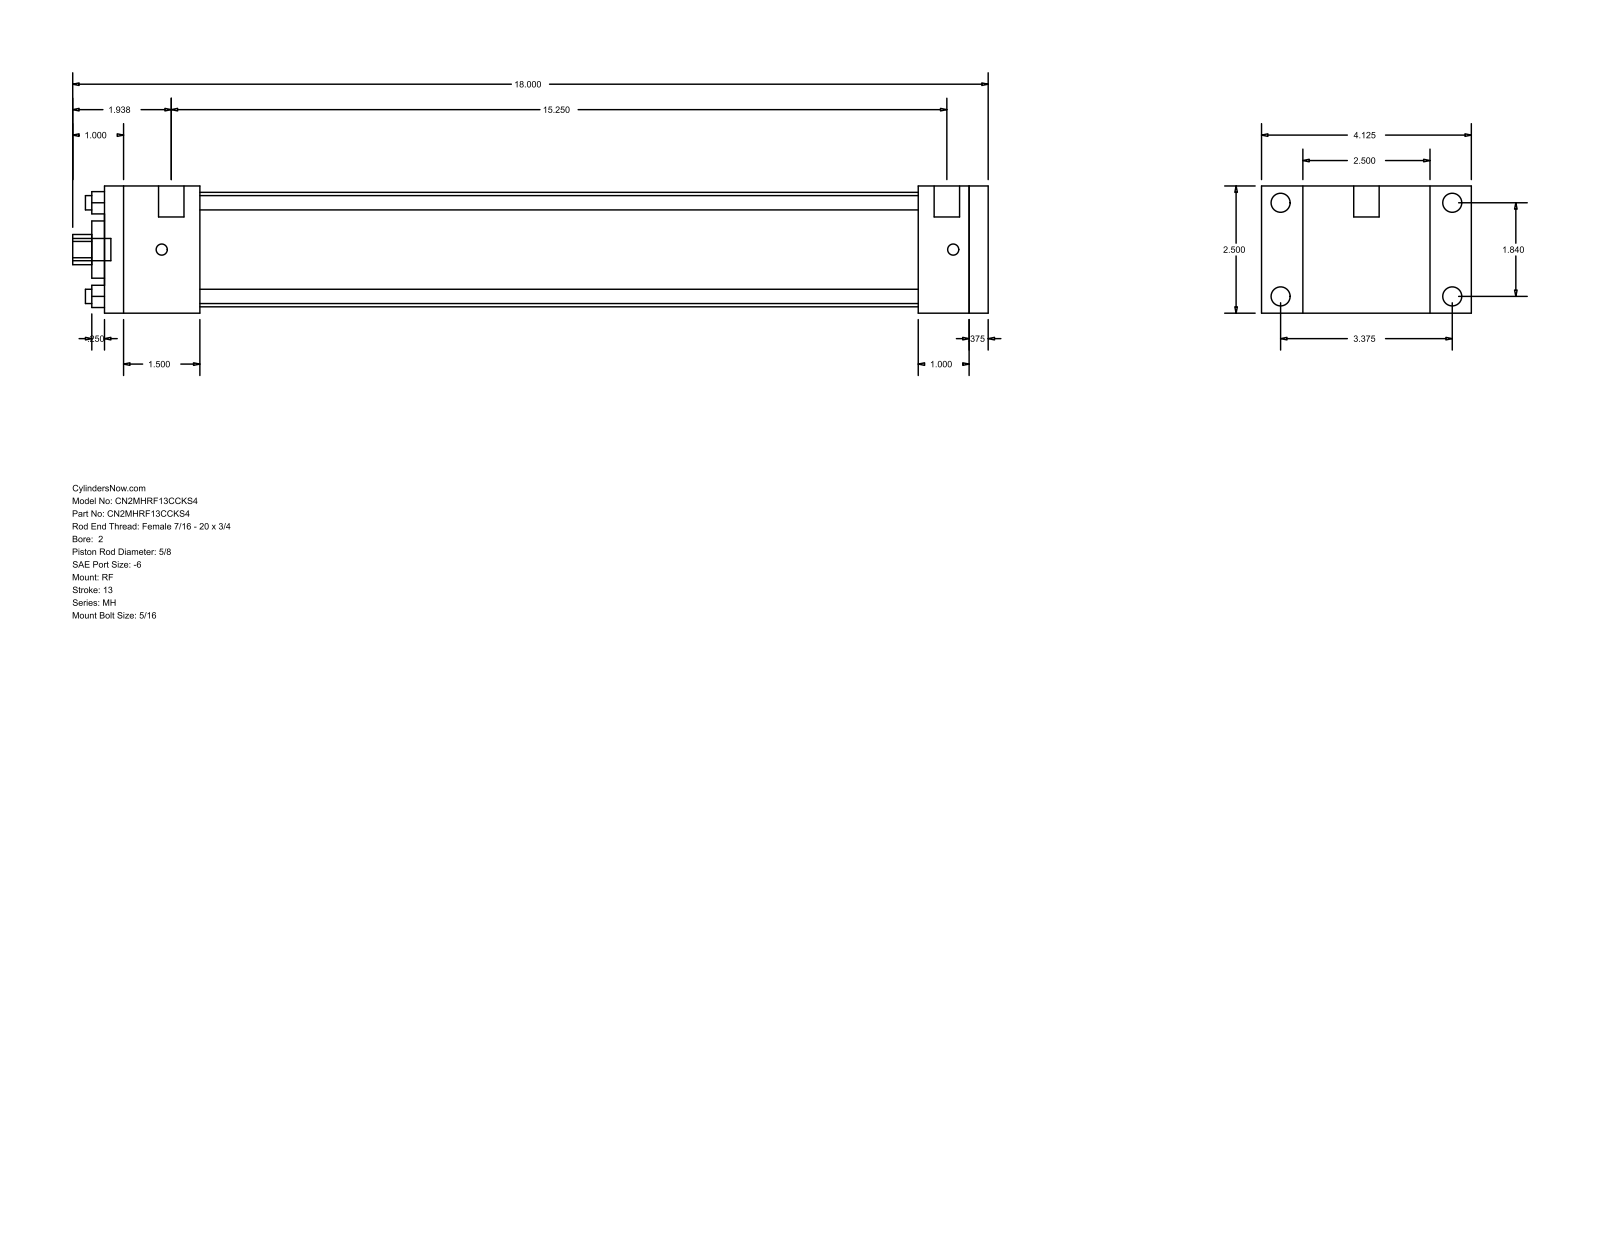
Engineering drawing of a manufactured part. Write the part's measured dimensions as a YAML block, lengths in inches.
part_name: "MH_RF__0200_0.625"
step_written_by: "GSSL Pune (CONFIG_CONTROL_DESIGN)"
units: inches
bodies: {solids: 0, faces: 92, planar: 64, cylindrical: 28, other: 0}
overall_size: [18, 4.125, 2.5]
round_holes:
  - {diameter: 0.281, count: 4}
  - {diameter: 0.625, count: 1}
  - {diameter: 1.125, count: 1}
  - {diameter: 2.25, count: 1}
round_bosses_or_shafts:
  - {diameter: 0.375, count: 4}
  - {diameter: 0.219, count: 4}
  - {diameter: 0.5, count: 2}
  - {diameter: 0.437, count: 1}
partial_cylinders:
  - {radius: 0.297, count: 1}
face_to_face_distances: [2.5, 17.375, 0.375, 17, 1.875, 16, 14.125, 15.125, 15.5, 1]
hole_center_spacings: [1.301, 1.84, 2.602]
